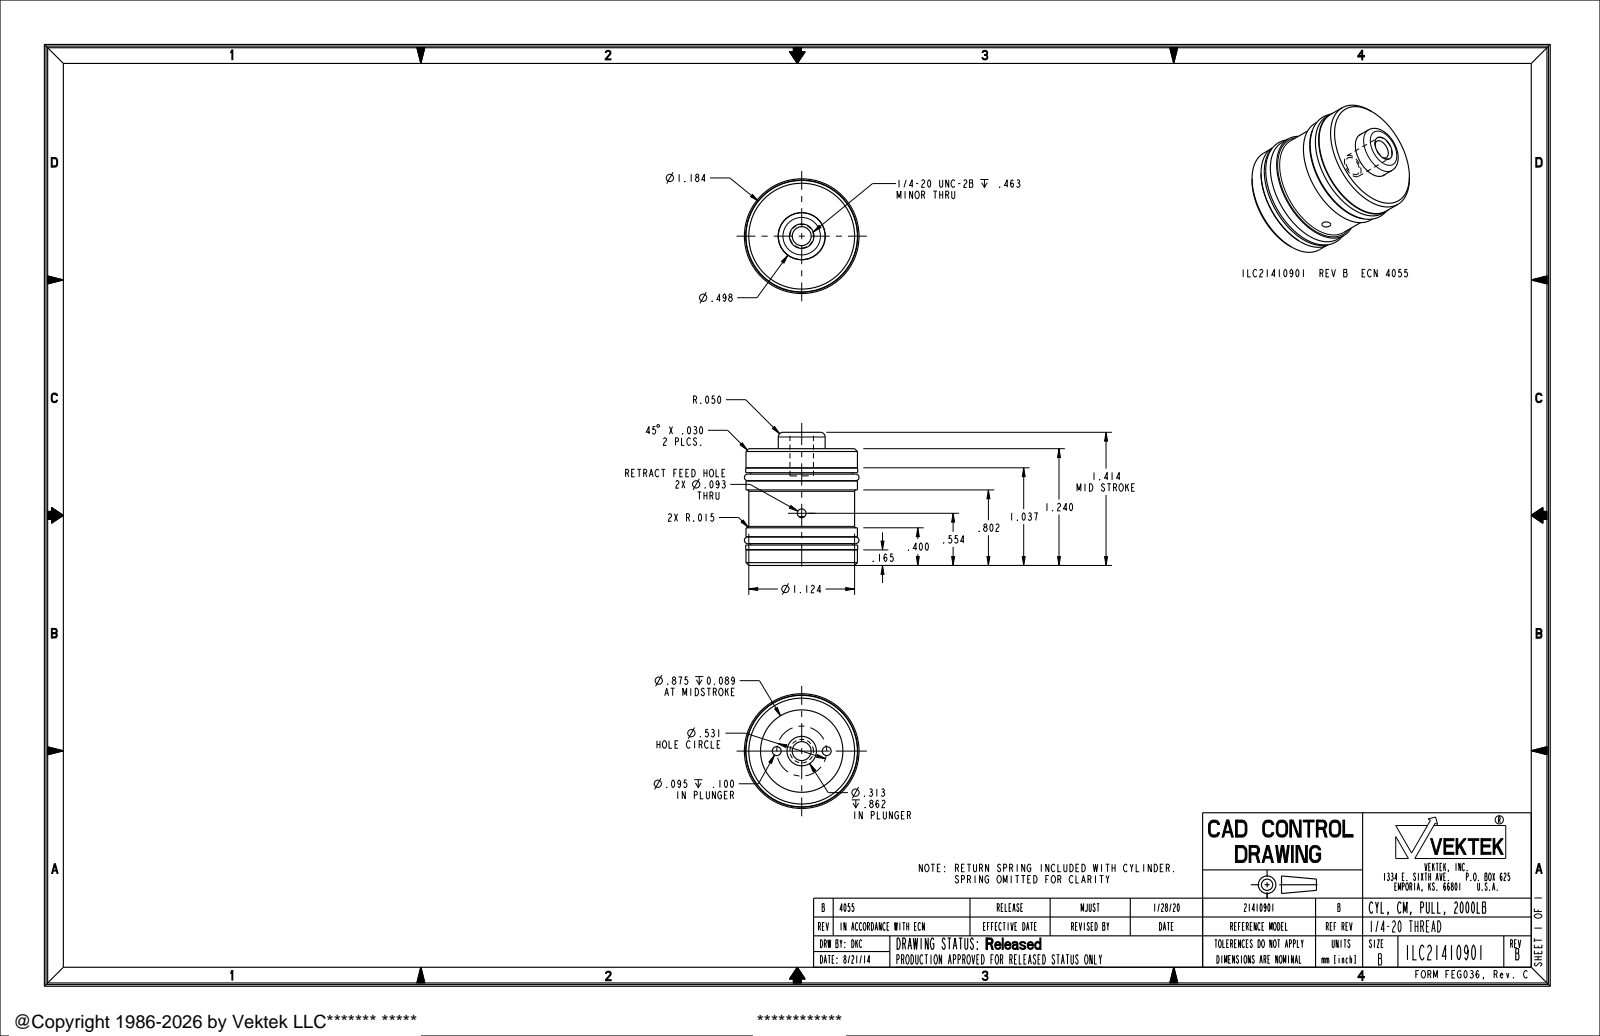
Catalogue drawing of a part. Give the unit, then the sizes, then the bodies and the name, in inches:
Units: inches
Overall size (bounding box): 1.414 × 1.218 × 1.218
Round holes (diameter × count): ⌀0.095 ×2, ⌀0.093 ×1, ⌀0.201 ×1, ⌀0.313 ×1, ⌀0.5 ×1, ⌀0.875 ×1
Round bosses / shafts (diameter × count): ⌀1.19 ×1, ⌀1.184 ×1, ⌀1.124 ×1, ⌀1.084 ×1, ⌀0.498 ×1, ⌀0.25 ×1
Main face-to-face distances: 0.088, 1.151, 0.429, 0.517, 0.634, 0.722, 1.24, 0.606, 0.518, 0.089
Hole centre spacings: 0.265, 0.531
Volume: 1.173 in³ · Surface area: 16.96 in²
Bodies: 2 solids, 84 faces (20 planar, 48 cylindrical, 16 other)
Part name (STEP PRODUCT): ILC21410901_BODY; ILC21410901_PLUNGER; ILC21410901
STEP written by: PRO/ENGINEER BY PARAMETRIC TECHNOLOGY CORPORATION, 2017170 (AUTOMOTIVE_DESIGN)
